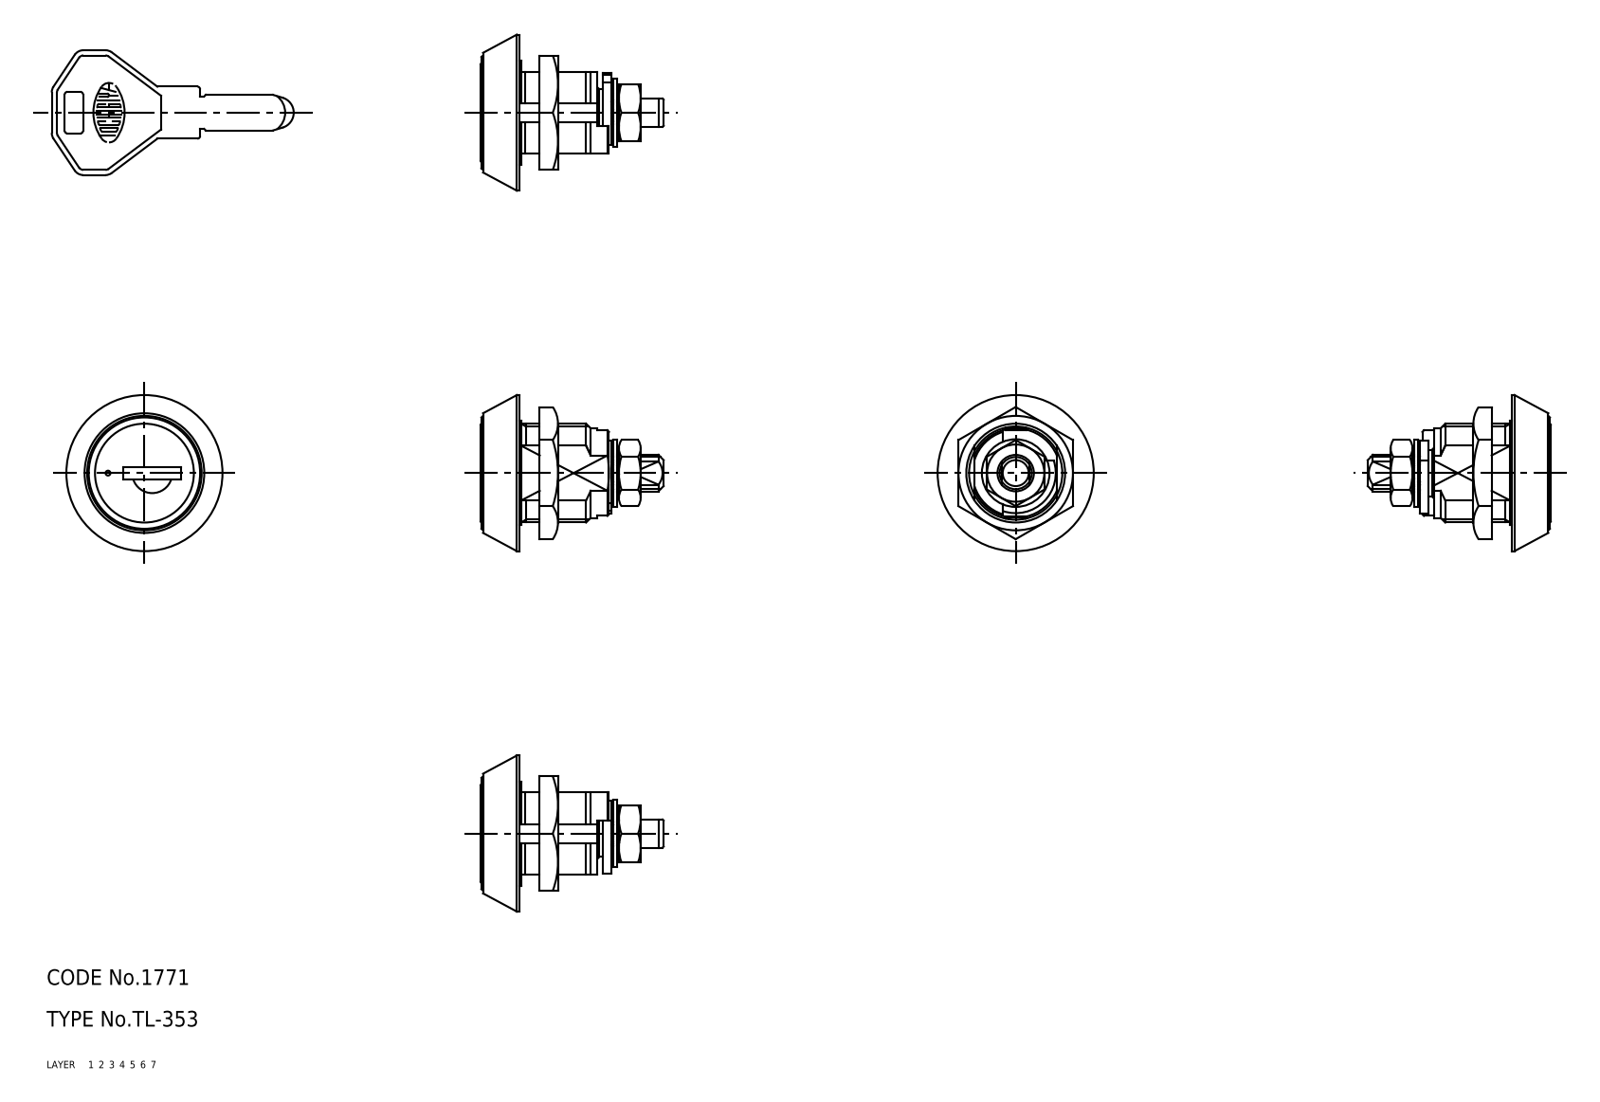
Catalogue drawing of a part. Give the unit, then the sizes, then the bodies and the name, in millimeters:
Units: millimetres
Overall size (bounding box): 117.58 × 30 × 30
Volume: 10 483 mm³ · Surface area: 9 162 mm²
Bodies: 8 solids, 187 faces (0 planar, 0 cylindrical, 187 other)
Part name (STEP PRODUCT): washer; ring; nut_B; nut_A (+4 more)
STEP written by: CADfix (AUTOMOTIVE_DESIGN)
